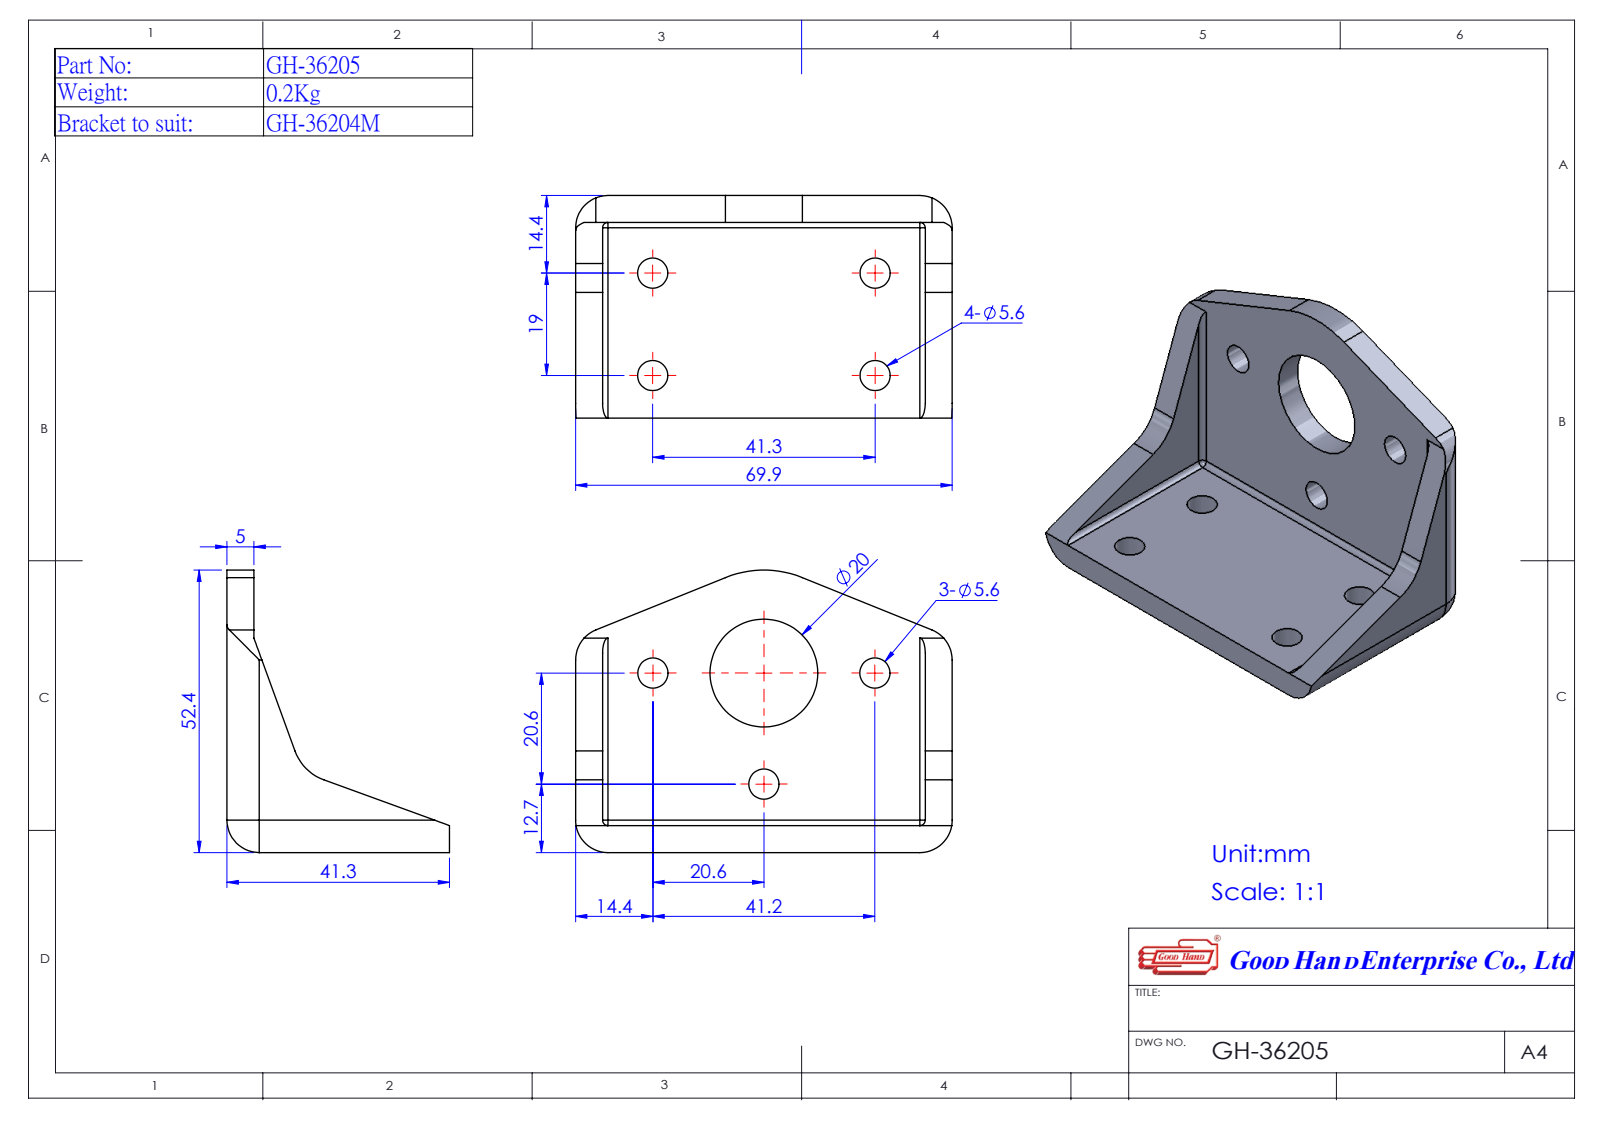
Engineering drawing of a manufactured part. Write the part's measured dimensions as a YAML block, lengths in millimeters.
part_name: "GH-36205; GH-36205 36205-1^493791(GH-36204M)"
step_written_by: "SolidWorks 2016 (AUTOMOTIVE_DESIGN)"
units: millimeters
bodies: {solids: 1, faces: 39, planar: 15, cylindrical: 24, other: 0}
overall_size: [69.9, 52.4, 41.3]
volume: 29430
surface_area: 14000
round_holes:
  - {diameter: 5.6, count: 7}
  - {diameter: 20, count: 1}
partial_cylinders:
  - {radius: 6, count: 3}
  - {radius: 1, count: 2}
  - {radius: 9, count: 1}
  - {radius: 19.1, count: 1}
face_to_face_distances: [5, 69.9, 64.9, 36.3, 41.3, 59.9]
hole_center_spacings: [20.6, 19, 29.13, 41.3, 45.46, 41.2]
